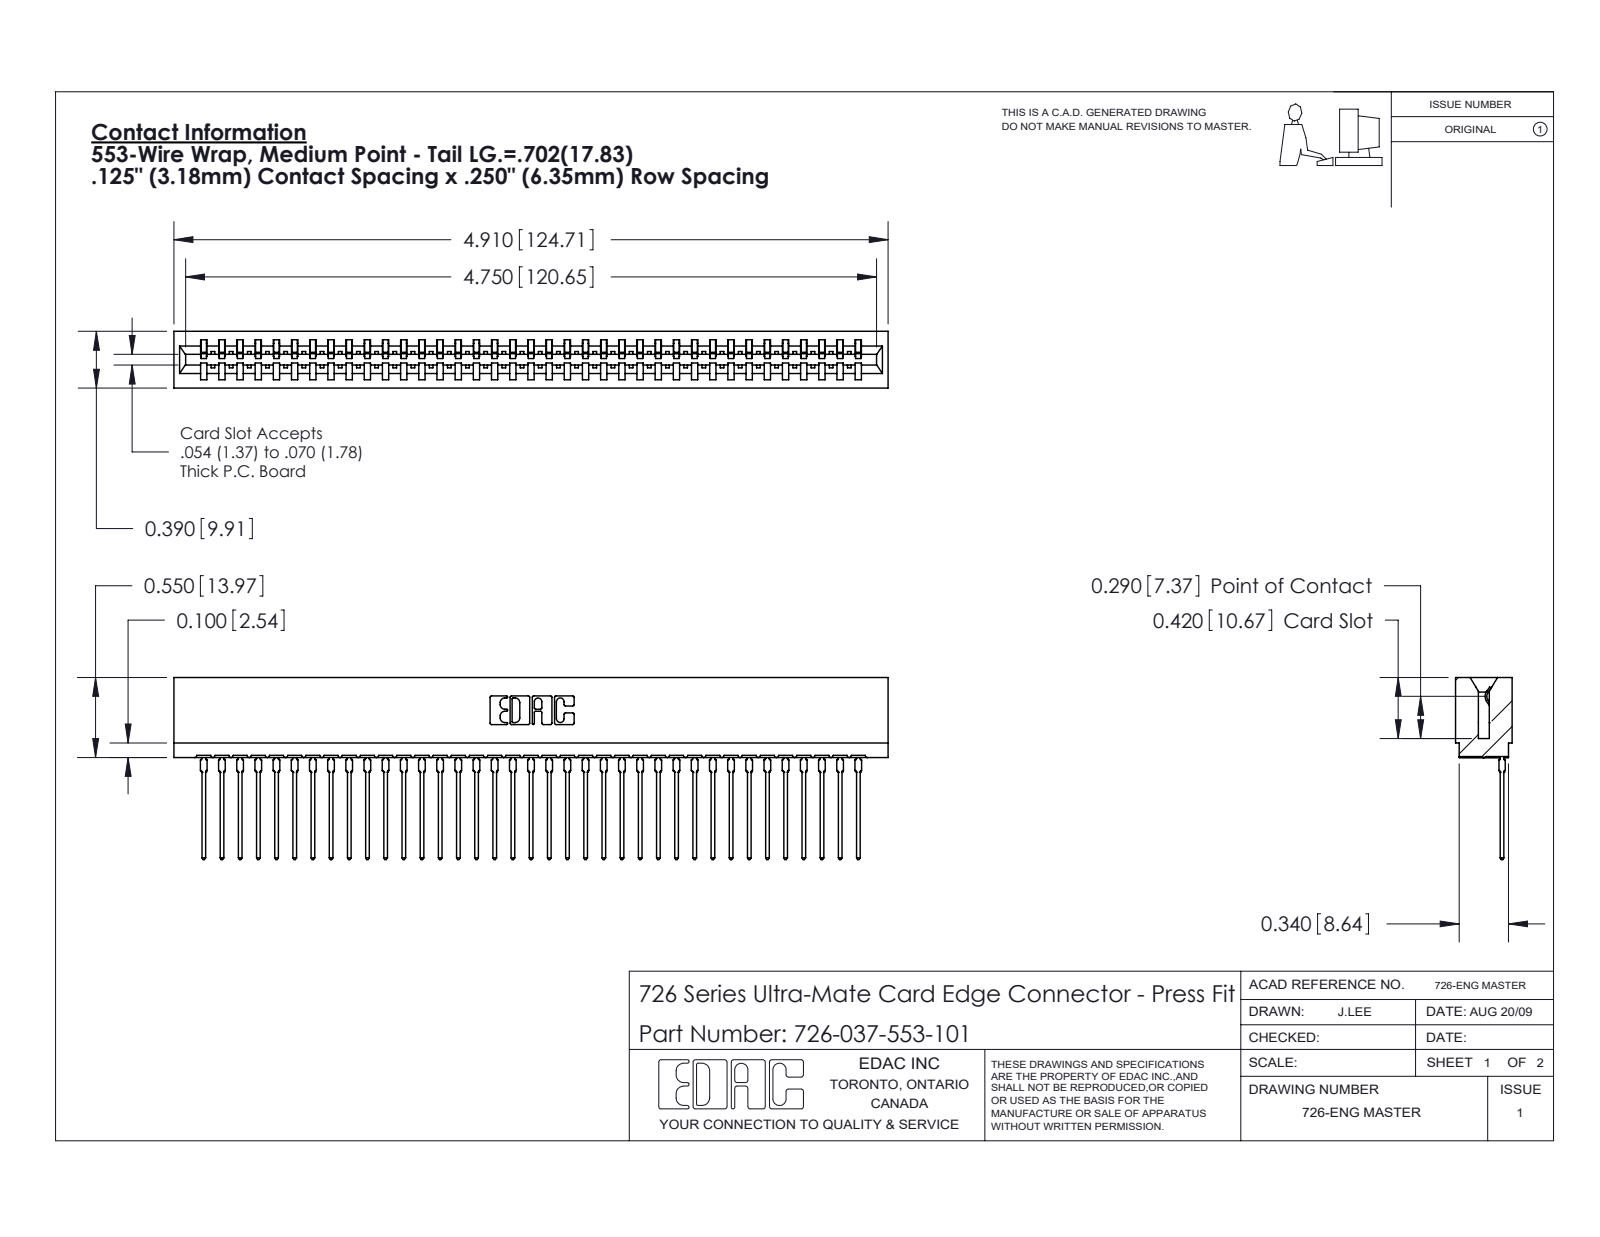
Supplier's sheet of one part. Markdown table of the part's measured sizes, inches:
| quantity | value |
| --- | --- |
| part name | 726 Part_.515 Slot Depth - 01; 726-037-553-101; 746-292-001_553 |
| STEP written by | SolidWorks 2020 (CONFIG_CONTROL_DESIGN) |
| units | inches |
| bodies | 38 solids, 4093 faces (2386 planar, 745 cylindrical, 962 other) |
| overall size | 4.91 × 1.251 × 0.39 |
| volume | 0.69 in³ |
| surface area | 27.68 in² |
| partial cylindrical surfaces (radius × count) | 0.021 × 74, 0.015 × 38, 0.01 × 22, 0.007 × 6, 0.031 × 6, 0.005 × 4, 0.011 × 4, 0.026 × 3 |
| main face-to-face distances | 0.057, 0.333, 0.25, 0.39, 0.025, 0.307, 0.083, 0.5, 0.275, 0.365 |
